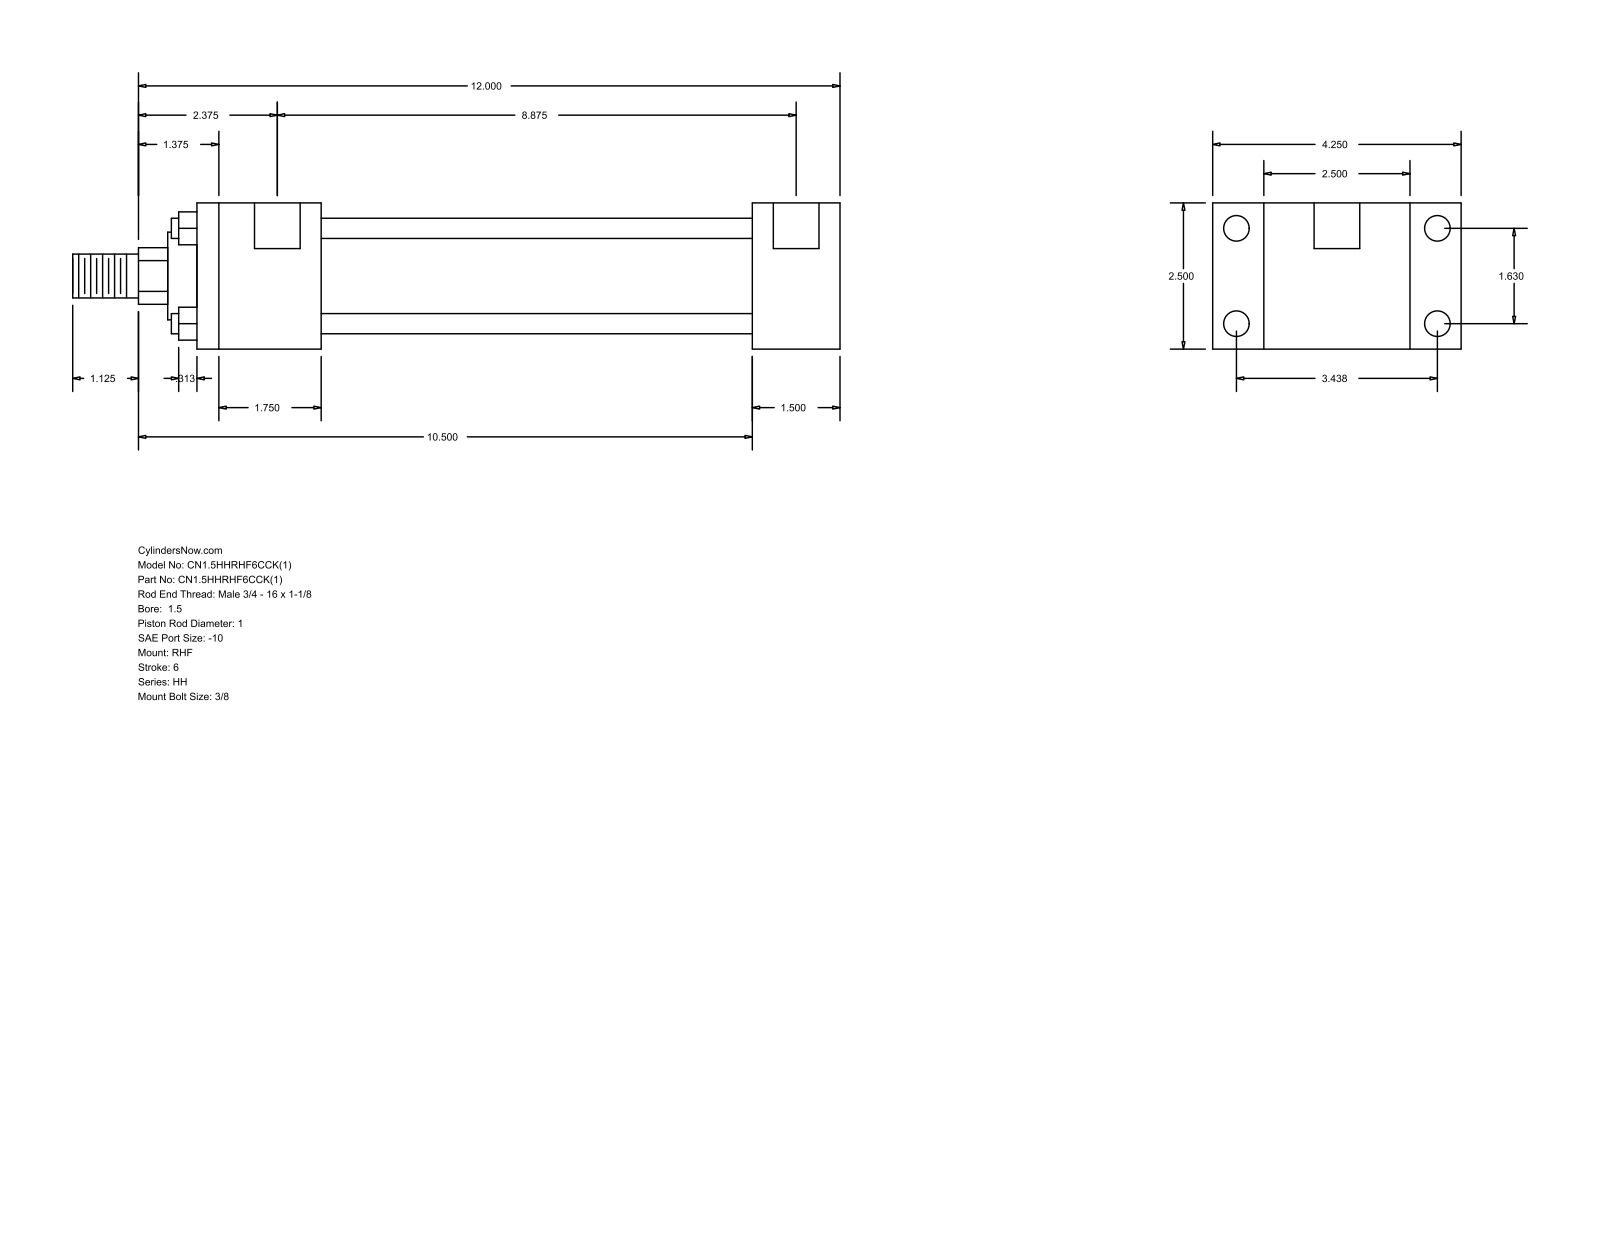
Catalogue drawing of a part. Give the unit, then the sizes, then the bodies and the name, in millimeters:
Units: millimetres
Overall size (bounding box): 333.38 × 107.95 × 63.5
Round holes (diameter × count): ⌀5.56 ×4, ⌀11.13 ×4, ⌀19.84 ×2
Round bosses / shafts (diameter × count): ⌀8.76 ×4, ⌀44.45 ×1, ⌀38.1 ×1, ⌀25.4 ×1, ⌀19.05 ×1
Partial cylindrical surfaces — rounded edges, fillets, slot ends (radius × count): R12.29 ×1
Main face-to-face distances: 63.5, 22.23, 85.73, 38.1, 107.96, 187.32, 225.42, 53.98, 241.3, 279.4
Hole centre spacings: 1.59, 41.4, 87.32, 96.64, 227.01, 228.6, 225.42
Bodies: 0 solids, 88 faces (60 planar, 28 cylindrical, 0 other)
Part name (STEP PRODUCT): HH_RHF__0150_1
STEP written by: GSSL Pune (CONFIG_CONTROL_DESIGN)
